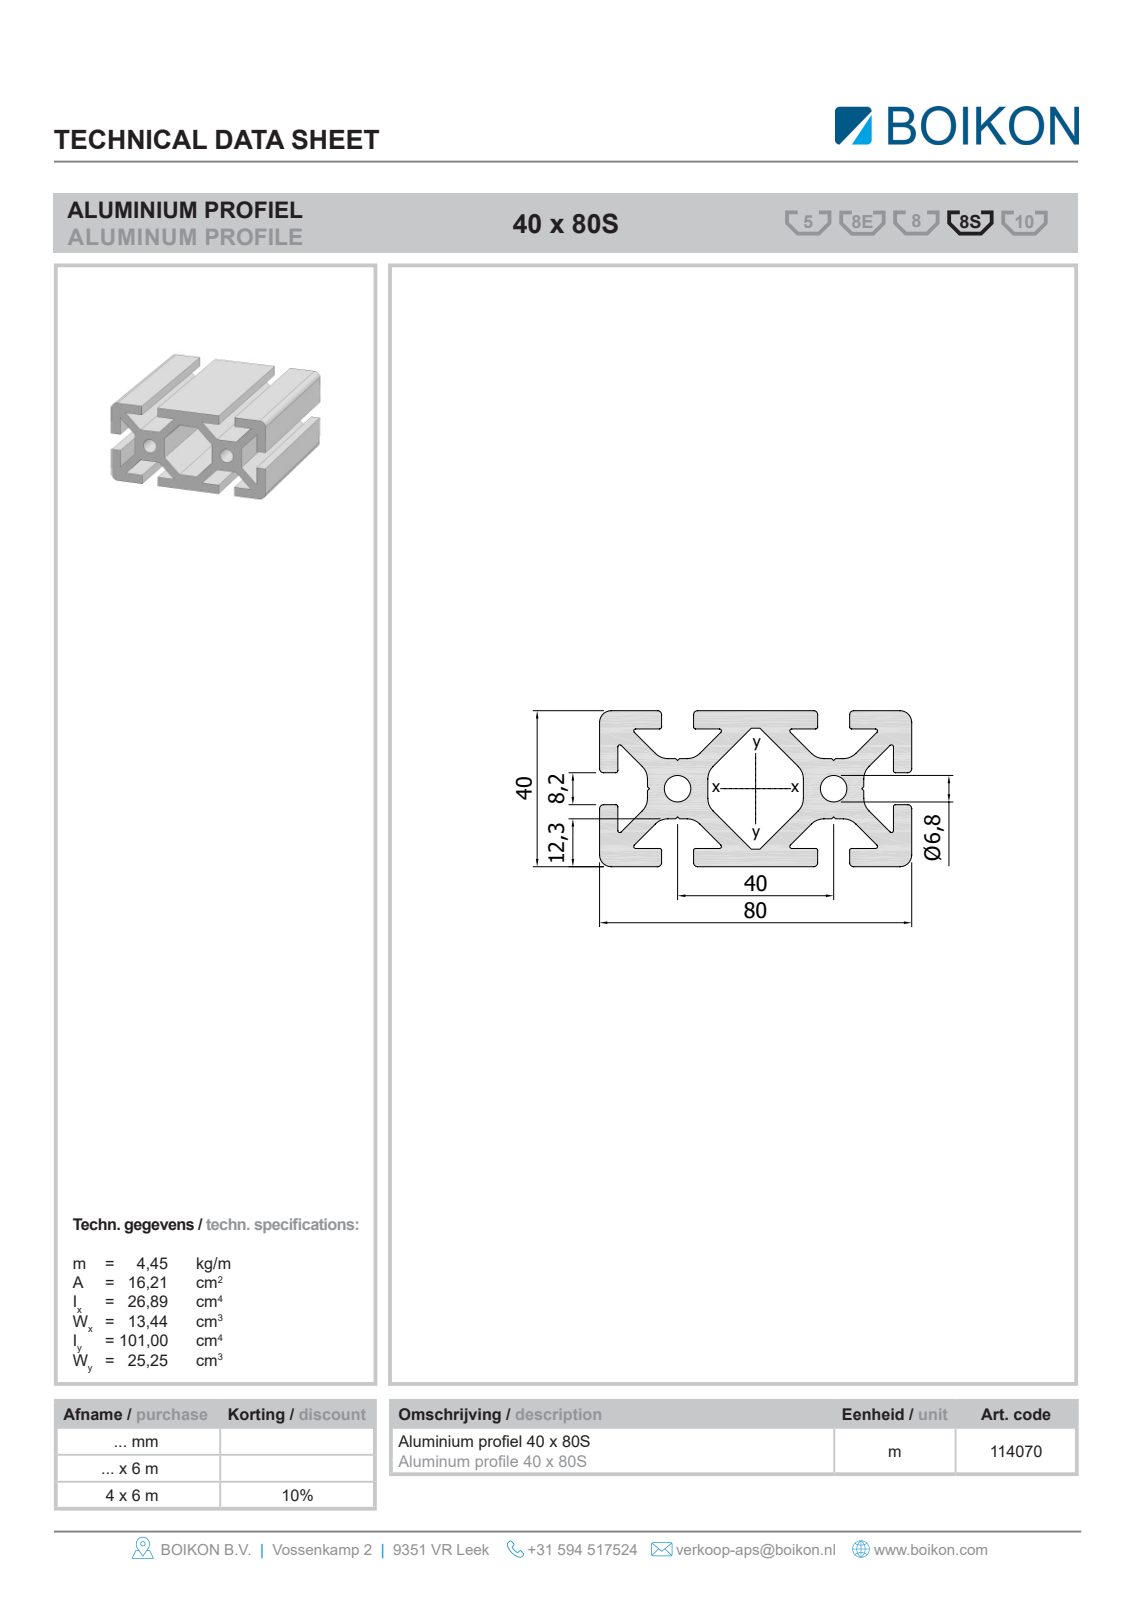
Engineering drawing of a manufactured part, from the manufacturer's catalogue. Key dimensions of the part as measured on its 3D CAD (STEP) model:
Part name (STEP PRODUCT): Root; 11407040x80SBOIKON0
STEP written by: HiCAD 2013 1802.4 Build 509 (AUTOMOTIVE_DESIGN)
Units: millimetres
Bodies: 1 solid, 68 faces (62 planar, 6 cylindrical, 0 other)
Overall size (bounding box): 1000 × 80 × 40
Volume: 1 579 000 mm³ · Surface area: 660 500 mm²
Round holes (diameter × count): ⌀6.8 ×2
Partial cylindrical surfaces — rounded edges, fillets, slot ends (radius × count): R3 ×4
Main face-to-face distances: 4.5, 40, 28.28, 4, 35.5, 12.25, 7.75, 27.75, 23.25, 3.65
Hole centre spacings: 40
